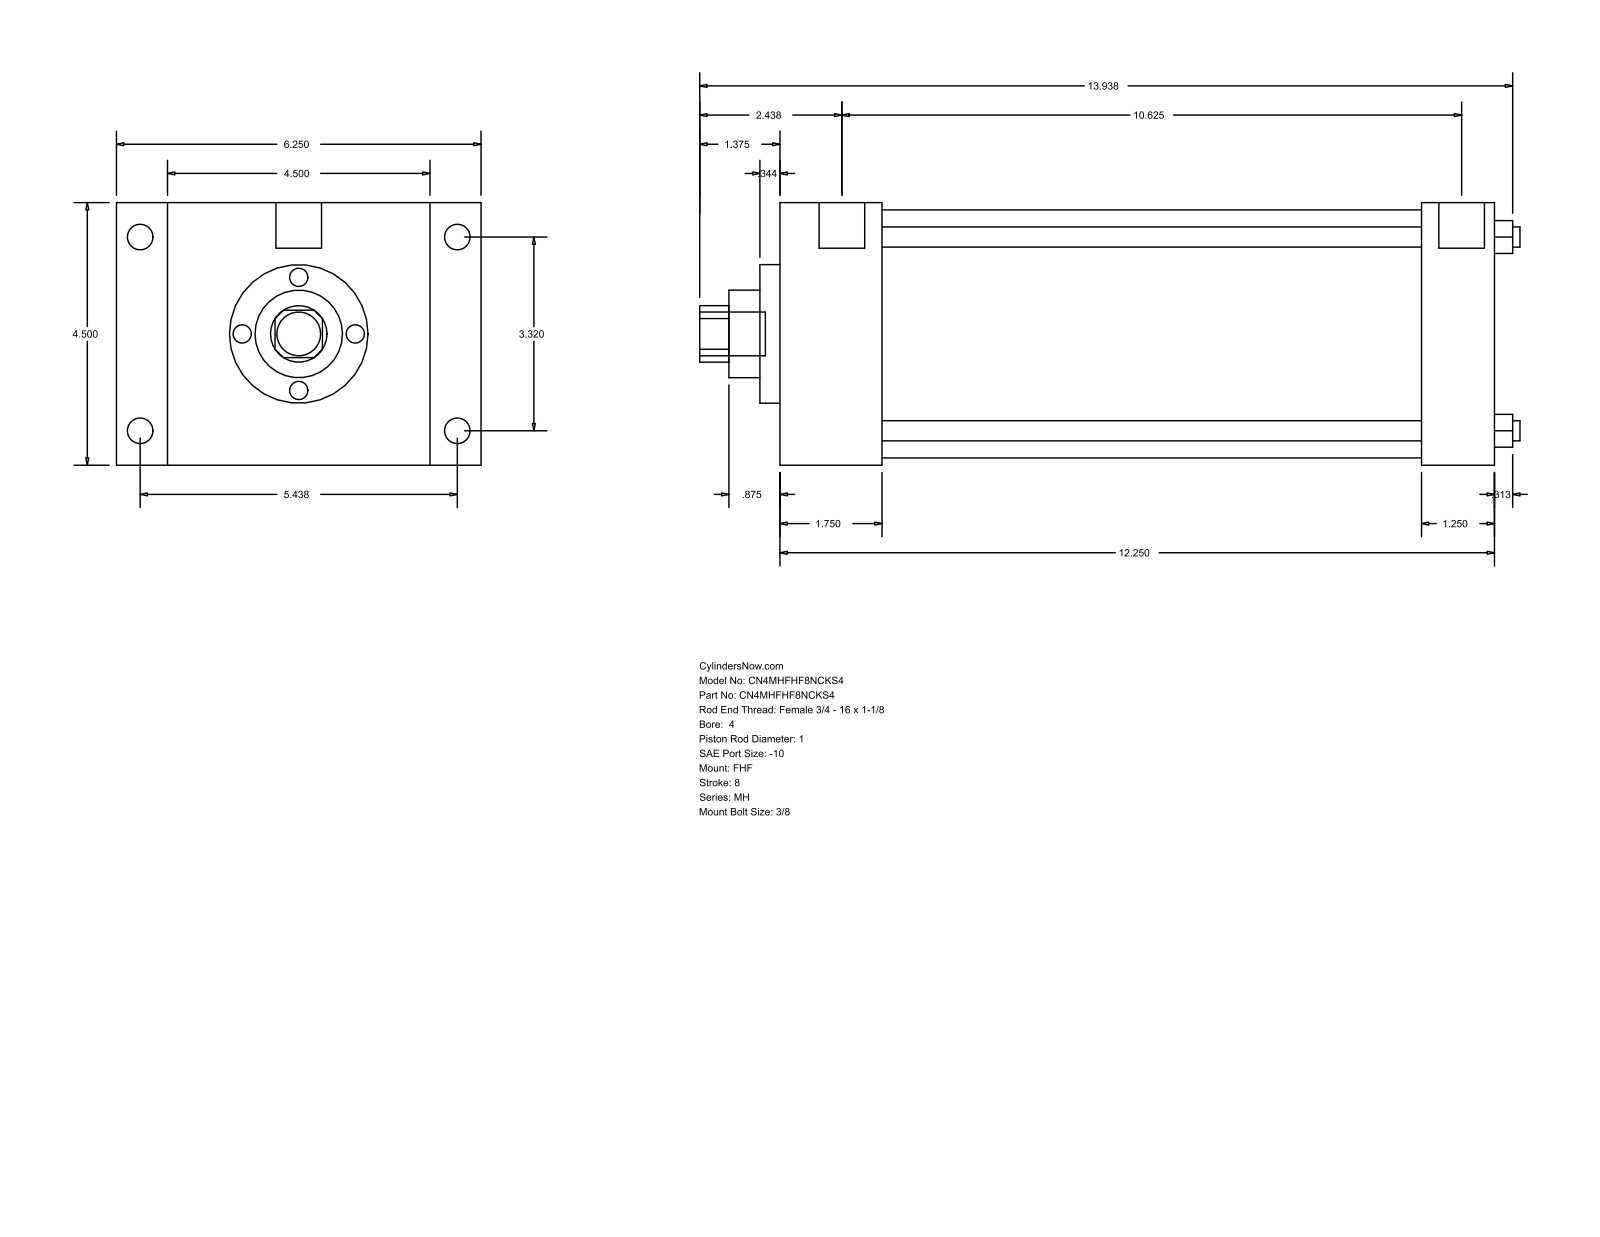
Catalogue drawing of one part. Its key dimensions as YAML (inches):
part_name: "MH_FHF__0400_1"
step_written_by: "GSSL Pune (CONFIG_CONTROL_DESIGN)"
units: inches
bodies: {solids: 0, faces: 90, planar: 61, cylindrical: 29, other: 0}
overall_size: [14.063, 6.25, 4.5]
round_holes:
  - {diameter: 0.345, count: 4}
  - {diameter: 1, count: 1}
  - {diameter: 1.5, count: 1}
  - {diameter: 2.375, count: 1}
  - {diameter: 4.25, count: 1}
round_bosses_or_shafts:
  - {diameter: 0.438, count: 4}
  - {diameter: 0.344, count: 4}
  - {diameter: 0.781, count: 2}
  - {diameter: 0.75, count: 1}
partial_cylinders:
  - {radius: 0.484, count: 1}
face_to_face_distances: [4.5, 12.25, 1.75, 10.5, 0.875, 5.375, 6.25, 11, 9.25, 1.25]
hole_center_spacings: [2.347, 3.32, 4.695]
